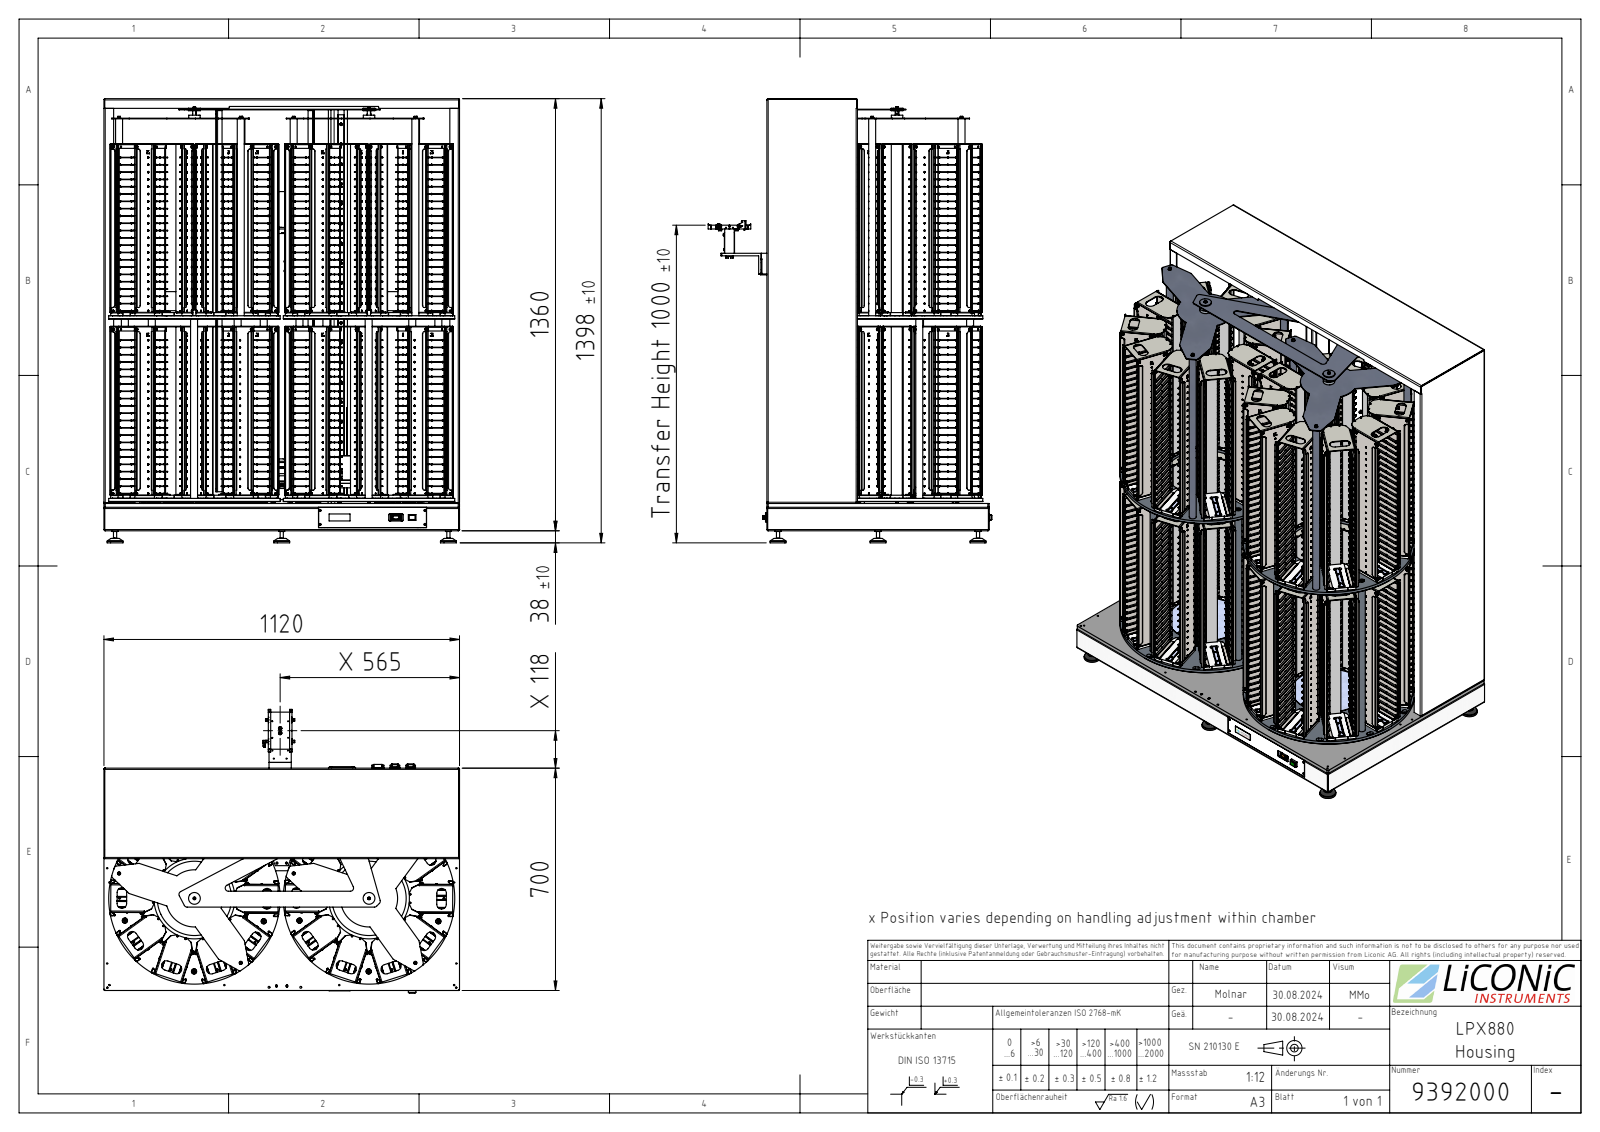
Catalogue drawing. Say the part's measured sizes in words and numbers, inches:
The part is named "9392000". Its 3-D file was written by "SolidWorks 2022 (AUTOMOTIVE_DESIGN)". It is 77 solids with 14078 faces: 7416 planar, 6464 cylindrical and 198 other. Overall it measures 55.039 by 44.094 by 35.196 inches. Its volume is 1 913 cubic inches and its surface area 21 960 square inches. Round holes: 176 of diameter 0.157, 78 of diameter 0.098, 73 of diameter 0.165, 51 of diameter 0.13, 28 of diameter 0.256, 16 of diameter 0.177, 16 of diameter 0.185, 16 of diameter 0.236, 16 of diameter 0.268, 16 of diameter 0.335, 12 of diameter 0.315, 10 of diameter 0.209. Round bosses or shafts: 16 of diameter 0.866, 7 of diameter 1.969, 7 of diameter 0.394, 3 of diameter 0.059, 2 of diameter 21.26, 2 of diameter 9.213, 1 of diameter 0.61, 1 of diameter 0.571. Partial cylindrical surfaces (rounded edges, fillets, slot ends): 1660 of radius 0.004, 1656 of radius 0.01, 840 of radius 0.079, 156 of radius 0.098, 133 of radius 0.197, 87 of radius 0.039, 44 of radius 0.059, 44 of radius 0.276. The main face-to-face distances are 0.079, 2.835, 0.394, 3.386, 44.016, 0.472, 2.913, 3.307, 22.638, 53.465. The hole center spacings are 0.906, 1.811, 2.717, 3.622, 4.528, 5.433, 6.339, 2.461.
